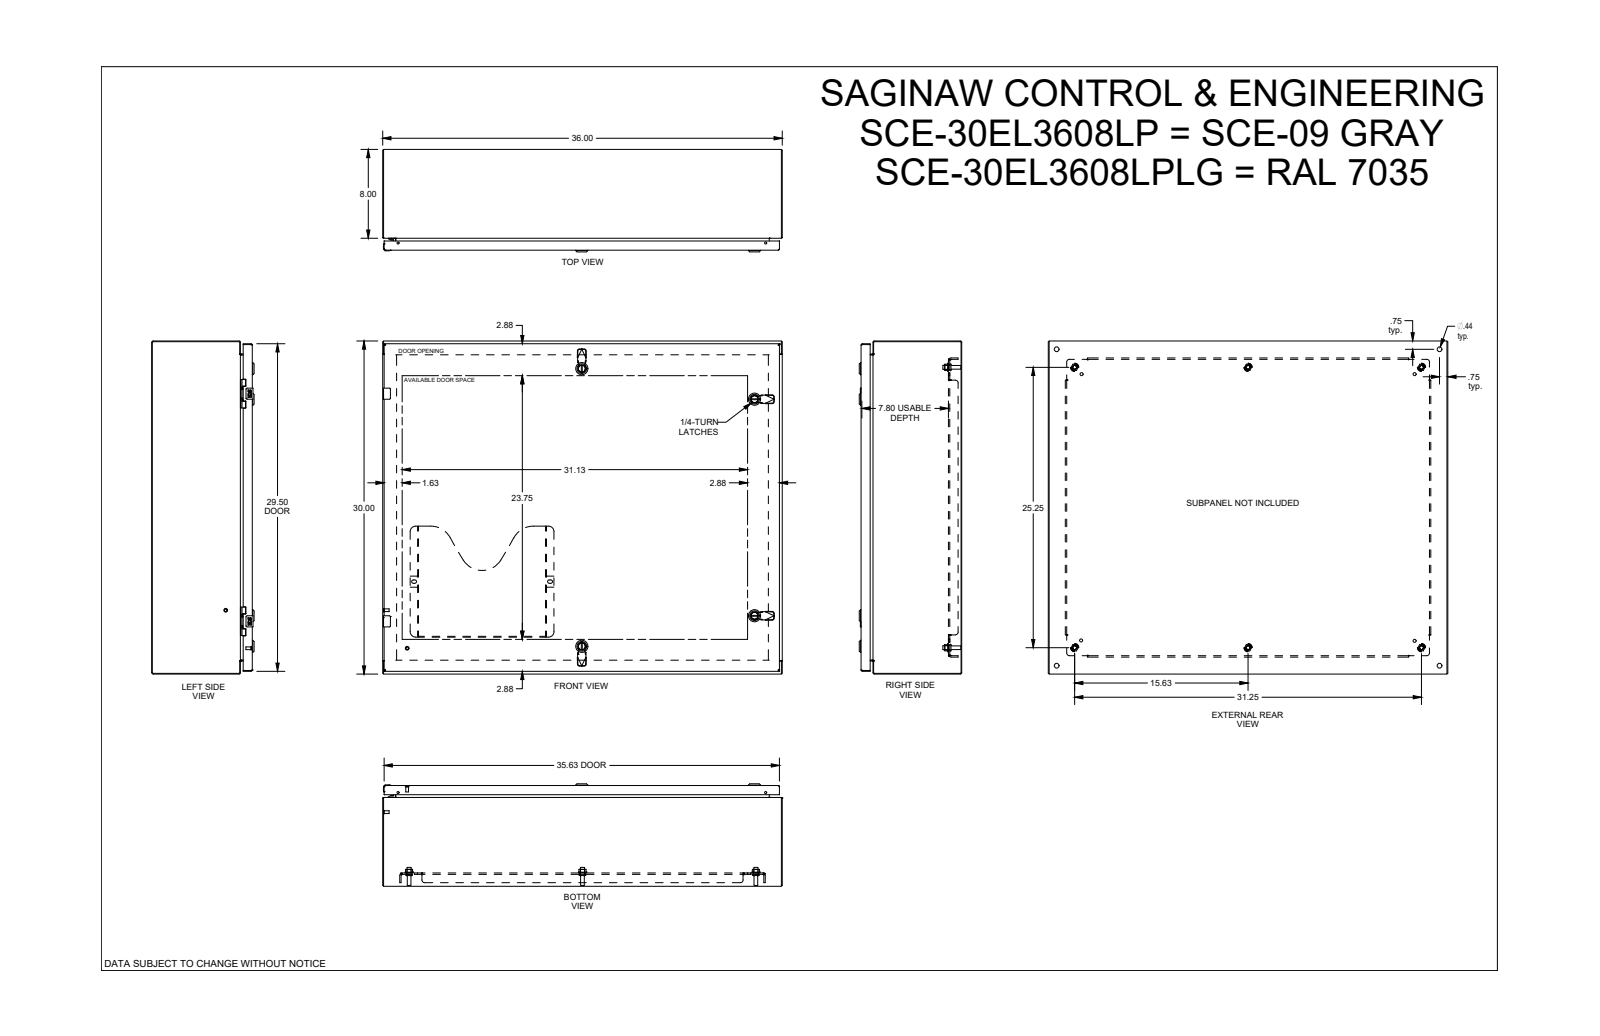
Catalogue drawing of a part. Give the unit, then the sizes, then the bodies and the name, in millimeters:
Units: millimetres
Overall size (bounding box): 914.4 × 762 × 234.4
Round holes (diameter × count): ⌀9.3 ×6, ⌀12.7 ×6, ⌀4.4 ×4, ⌀5 ×4, ⌀5.2 ×4, ⌀6.2 ×4, ⌀6.8 ×4, ⌀7.1 ×4, ⌀8 ×4, ⌀9.5 ×4, ⌀10 ×4, ⌀11.1 ×4
Round bosses / shafts (diameter × count): ⌀9.3 ×6, ⌀8.4 ×6, ⌀4.3 ×6, ⌀28 ×4, ⌀19.8 ×4, ⌀16 ×4, ⌀13.5 ×4, ⌀12.8 ×4
Partial cylindrical surfaces — rounded edges, fillets, slot ends (radius × count): R0.3 ×110, R0.5 ×44, R0.3 ×40, R0.4 ×20, R1 ×17, R4 ×16, R1.5 ×13, R0.7 ×12
Main face-to-face distances: 1.9, 228.5, 1.5, 230.5, 228.9, 227, 28.6, 30.5, 200, 3.2
Hole centre spacings: 25, 520.7, 0.5, 12.5, 12.5, 114.1, 440.1, 836.1
Volume: 6 702 000 mm³ · Surface area: 6 207 000 mm²
Bodies: 61 solids, 3703 faces (1465 planar, 1168 cylindrical, 1070 other)
Part name (STEP PRODUCT): SCE-30EL3608LP
STEP written by: SolidWorks 2021 (AUTOMOTIVE_DESIGN)
